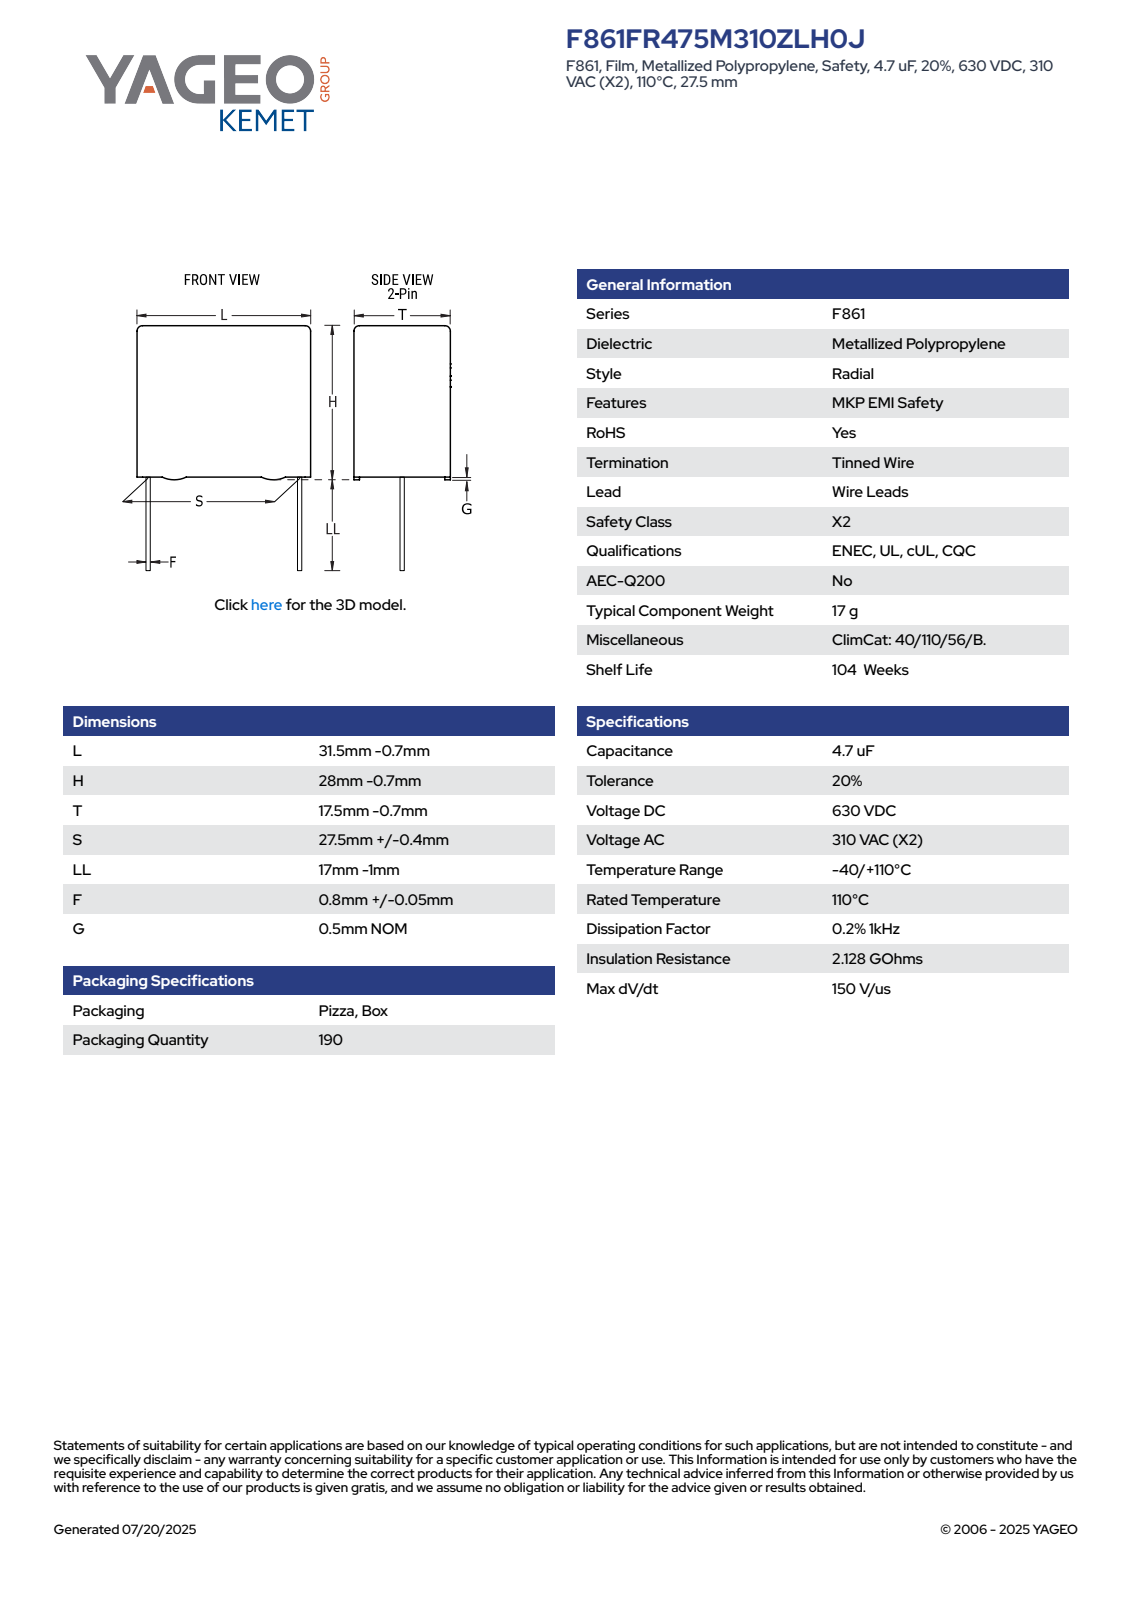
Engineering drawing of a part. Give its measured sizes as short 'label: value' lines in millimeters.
name: CFR_RBG_31.5X28X17.5_L30.8H27.3T16.8S27.5LL16F0.85G0.5
written by: SolidWorks 2014 (AUTOMOTIVE_DESIGN)
unit: mm
bodies: 4 solids, 89 faces (81 planar, 8 cylindrical, 0 other)
size: 43.3 × 30.8 × 16.8
volume: 13 891 mm³; area: 3 778 mm²
bosses: 2× ⌀0.85
rounds: 4× R0.5
face distances: 16.8, 26.8, 30.8, 16.81, 0.5, 27.3, 0.96, 15.84, 0.97, 14.88
